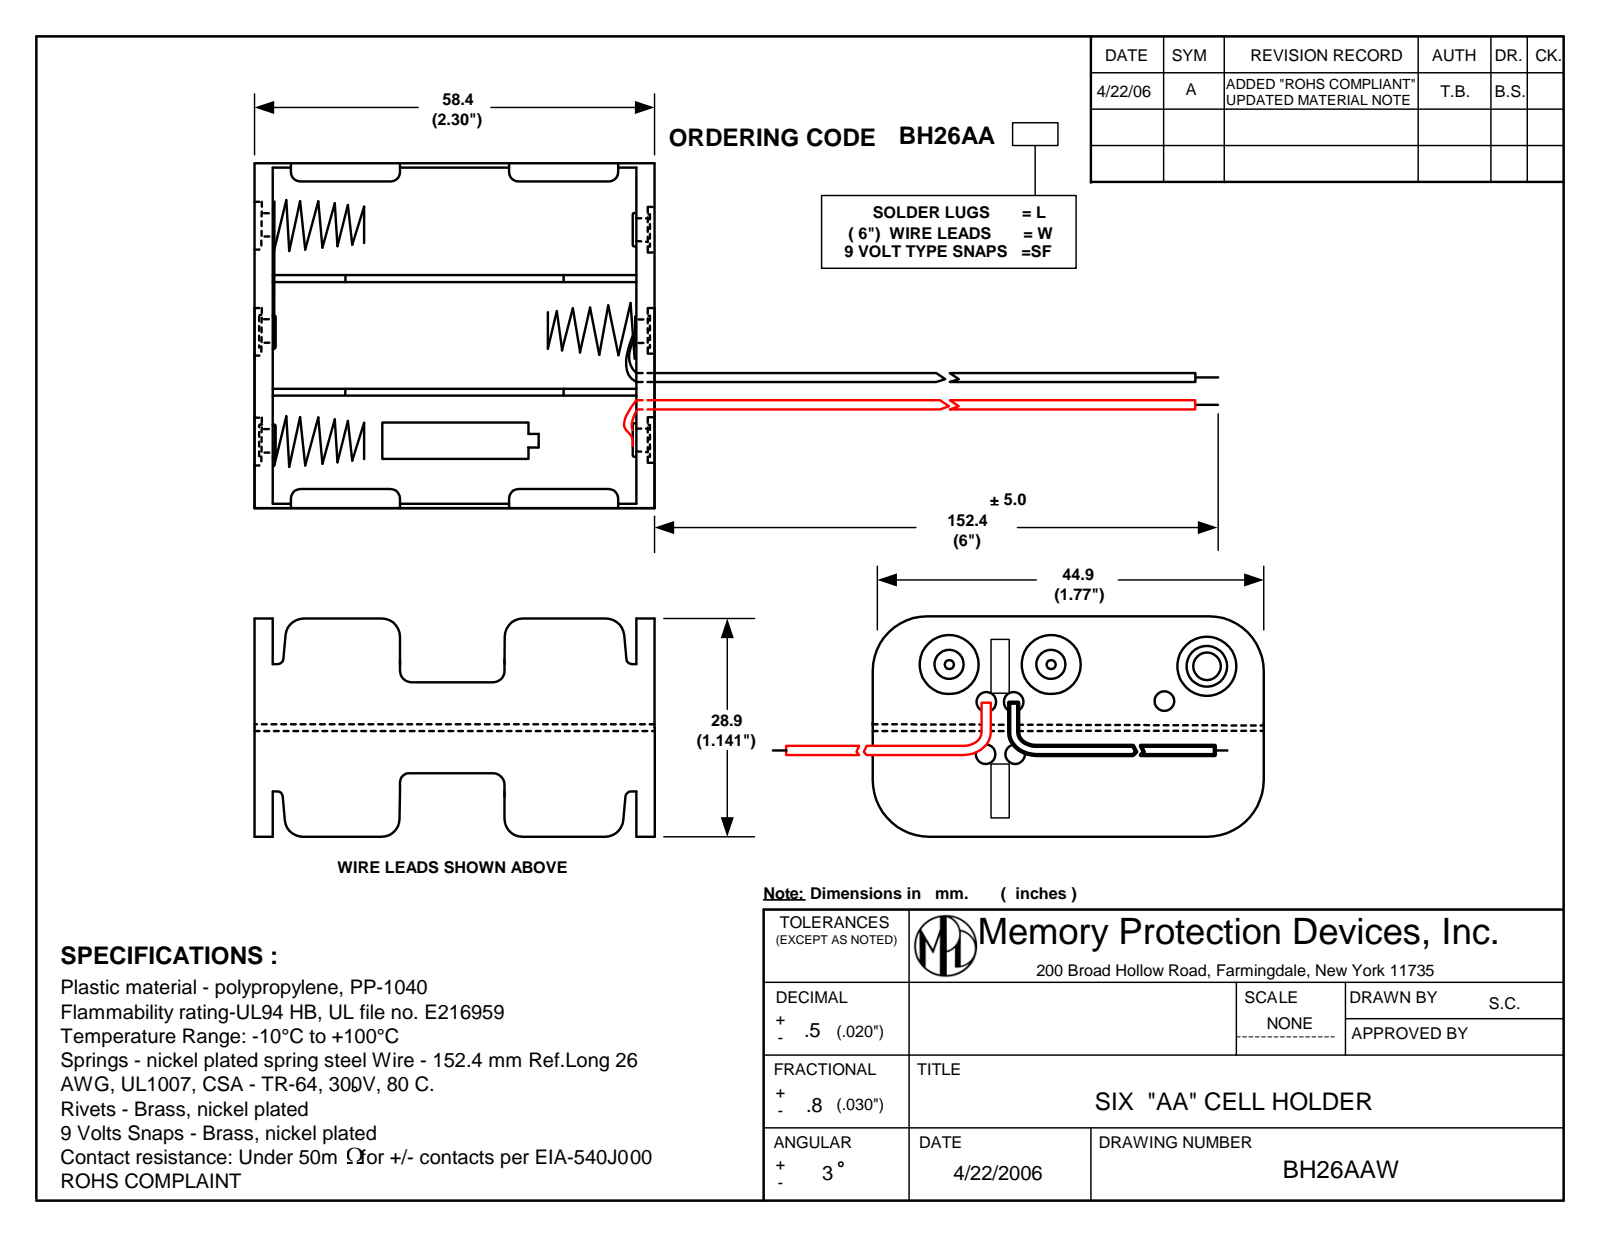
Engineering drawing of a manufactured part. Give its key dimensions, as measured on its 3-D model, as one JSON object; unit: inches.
{"part_name": "BH26AAW", "step_written_by": "SolidWorks 2017 (AUTOMOTIVE_DESIGN)", "units": "inches", "bodies": {"solids": 17, "faces": 771, "planar": 351, "cylindrical": 272, "other": 148}, "overall_size": [8.205, 1.772, 1.142], "volume_in3": 0.86, "surface_area_in2": 31.32, "round_holes": [[0.063, 6], [0.091, 6], [0.118, 6], [0.146, 6], [0.319, 6], [0.079, 5], [0.016, 2]], "round_bosses_or_shafts": [[0.244, 6], [0.185, 6], [0.138, 6], [0.024, 4], [0.032, 2]], "partial_cylinders_radius": [[0.098, 16], [0.197, 4], [0.275, 4], [0.308, 4]], "face_to_face_distances": [0.043, 0.122, 2.256, 2.213, 2.299, 1.728, 0.586, 1.142, 1.143, 0.586], "hole_center_spacings": [0.264, 0.474, 0.388, 0.553, 0.556, 0.646, 0.91, 0.991]}
